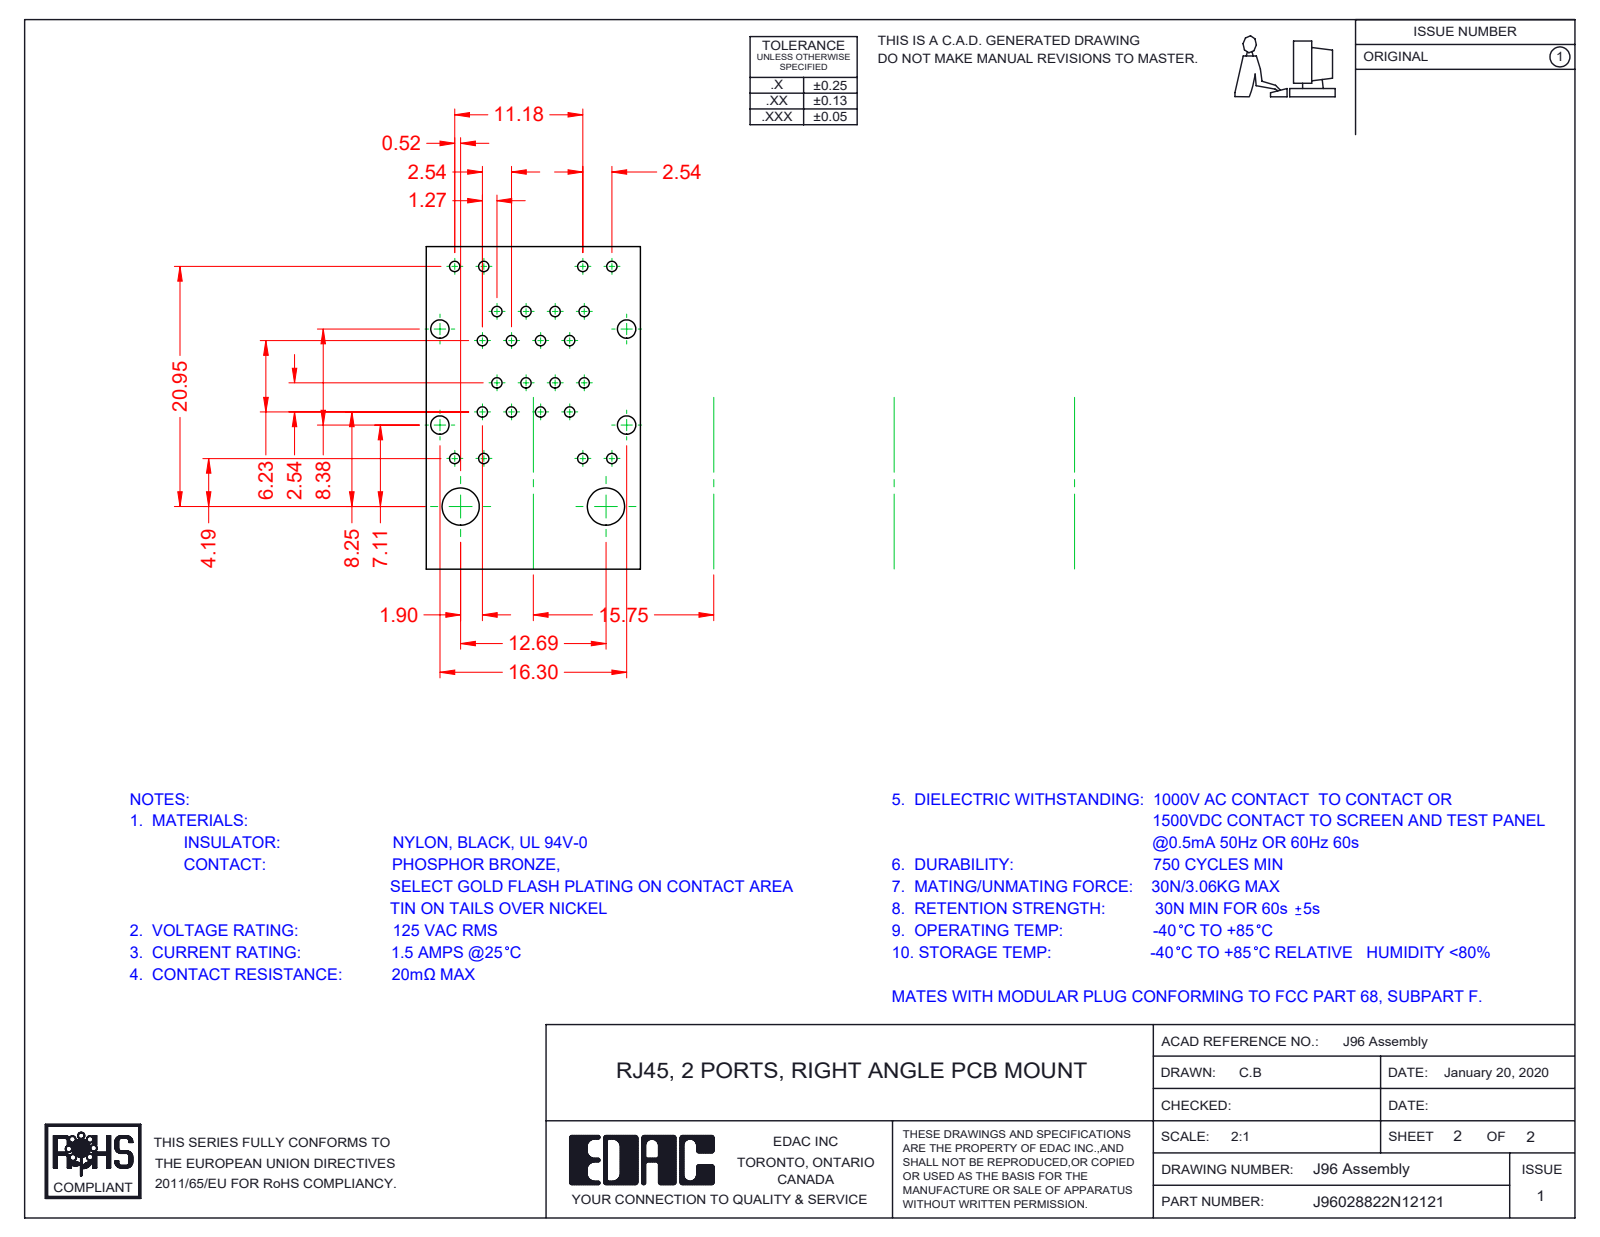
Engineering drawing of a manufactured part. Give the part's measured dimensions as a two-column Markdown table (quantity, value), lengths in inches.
| quantity | value |
| --- | --- |
| part name | J96028822N12121; 96 Contacts Lower; 96 Contacts Upper; 96 LED RH Upper_2-Red (+8 more) |
| STEP written by | SolidWorks 2016 (CONFIG_CONTROL_DESIGN) |
| units | inches |
| bodies | 27 solids, 2382 faces (1849 planar, 427 cylindrical, 106 other) |
| overall size | 1.165 × 1.129 × 0.661 |
| volume | 0.418 in³ |
| surface area | 29.62 in² |
| partial cylindrical surfaces (radius × count) | 0.01 × 48, 0.006 × 32, 0.014 × 24, 0.02 × 16, 0.039 × 16, 0.008 × 13, 0.028 × 9, 0.079 × 5 |
| main face-to-face distances | 0.642, 0.634, 0.069, 0.65, 0.581, 0.061, 0.573, 0.021, 0.058, 0.441 |
